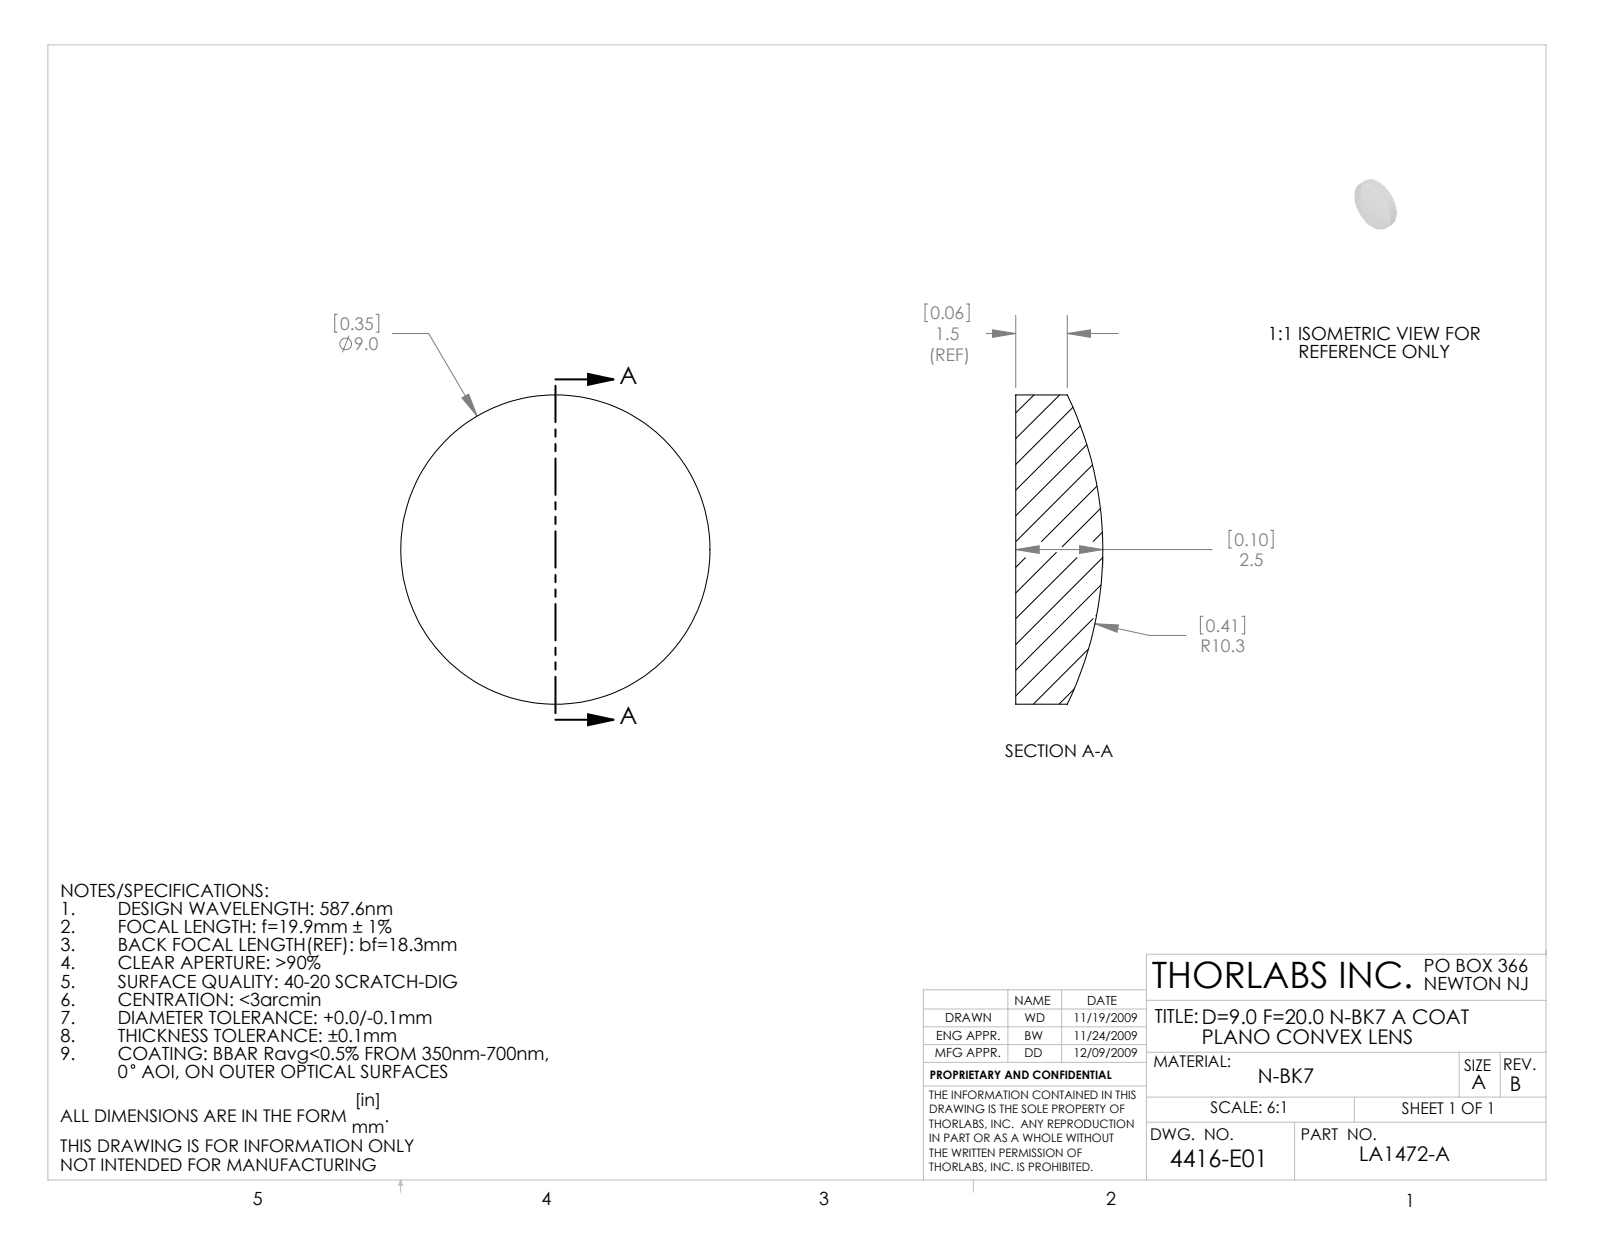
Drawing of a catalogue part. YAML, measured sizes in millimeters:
part_name: "4416-E0W"
step_written_by: "SolidWorks 2009 (AUTOMOTIVE_DESIGN)"
units: millimeters
bodies: {solids: 1, faces: 5, planar: 1, cylindrical: 2, other: 2}
overall_size: [9, 9, 2.53]
volume: 129
surface_area: 173
round_bosses_or_shafts:
  - {diameter: 9, count: 1}
